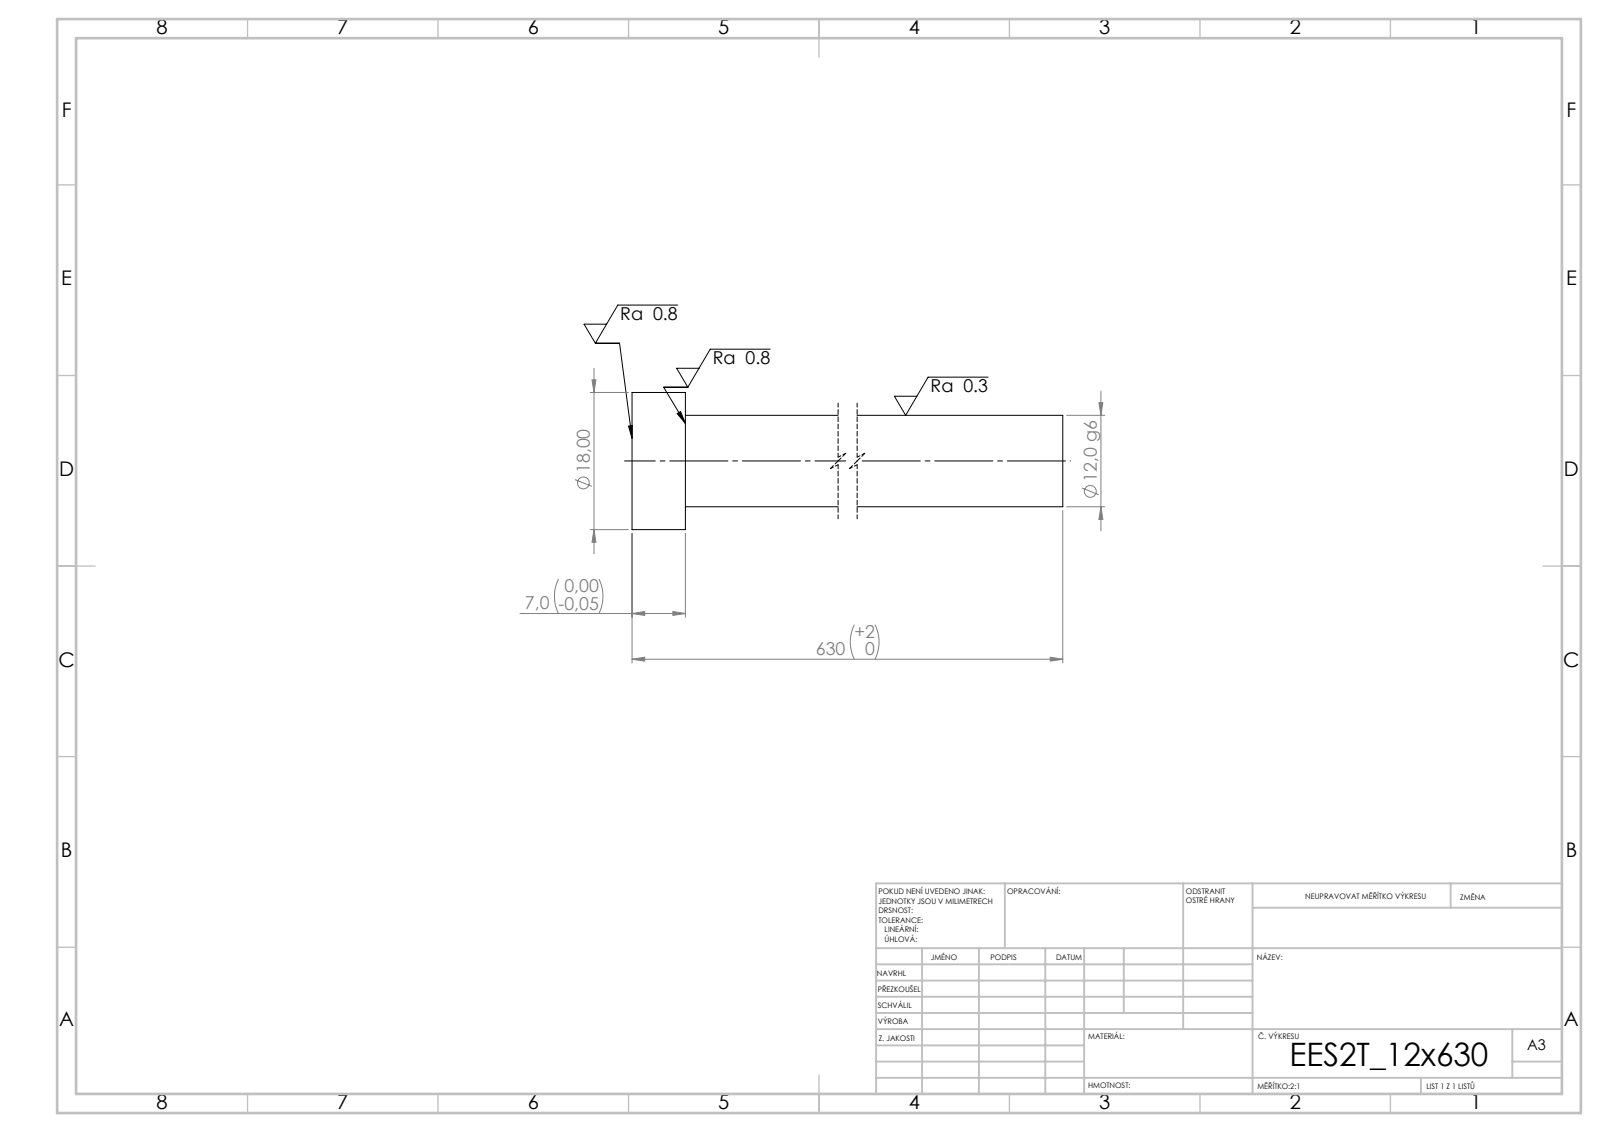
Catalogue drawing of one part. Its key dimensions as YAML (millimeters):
step_written_by: "SolidWorks 2019 (CONFIG_CONTROL_DESIGN)"
units: millimeters
bodies: {solids: 1, faces: 7, planar: 3, cylindrical: 4, other: 0}
overall_size: [630, 18, 18]
volume: 72241
surface_area: 24391
round_bosses_or_shafts:
  - {diameter: 18, count: 1}
  - {diameter: 12, count: 1}
face_to_face_distances: [7, 630, 623]
